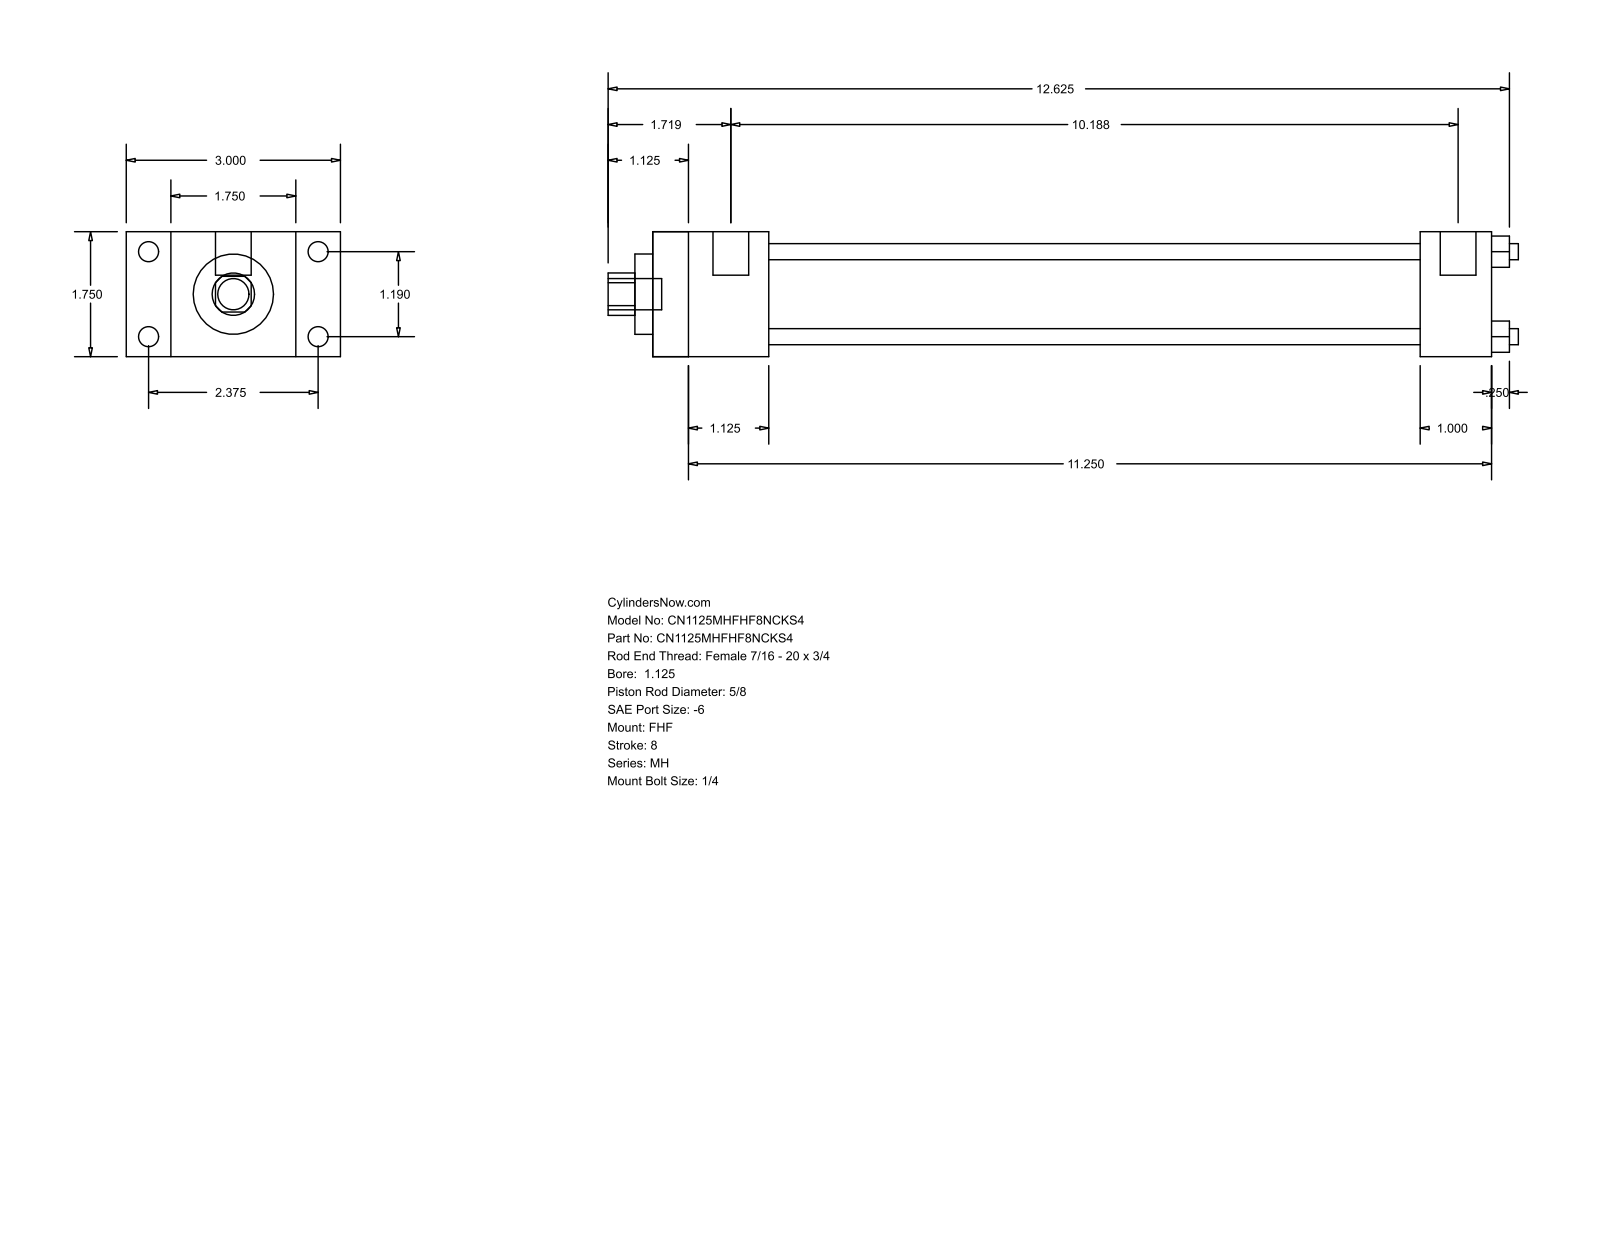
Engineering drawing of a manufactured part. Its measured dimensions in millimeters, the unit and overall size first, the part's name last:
Units: millimetres
Overall size (bounding box): 323.85 × 76.2 × 44.45
Round holes (diameter × count): ⌀5.71 ×4, ⌀15.88 ×1, ⌀28.57 ×1, ⌀34.92 ×1
Round bosses / shafts (diameter × count): ⌀7.14 ×4, ⌀5.56 ×4, ⌀12.7 ×2, ⌀11.11 ×1
Partial cylindrical surfaces — rounded edges, fillets, slot ends (radius × count): R7.54 ×1
Main face-to-face distances: 44.46, 15.87, 60.33, 41.27, 76.2, 298.44, 257.17, 273.05, 231.78, 25.39
Hole centre spacings: 21.37, 30.22, 42.74
Bodies: 0 solids, 88 faces (60 planar, 28 cylindrical, 0 other)
Part name (STEP PRODUCT): MH_FHF__0112_0.625
STEP written by: GSSL Pune (CONFIG_CONTROL_DESIGN)
